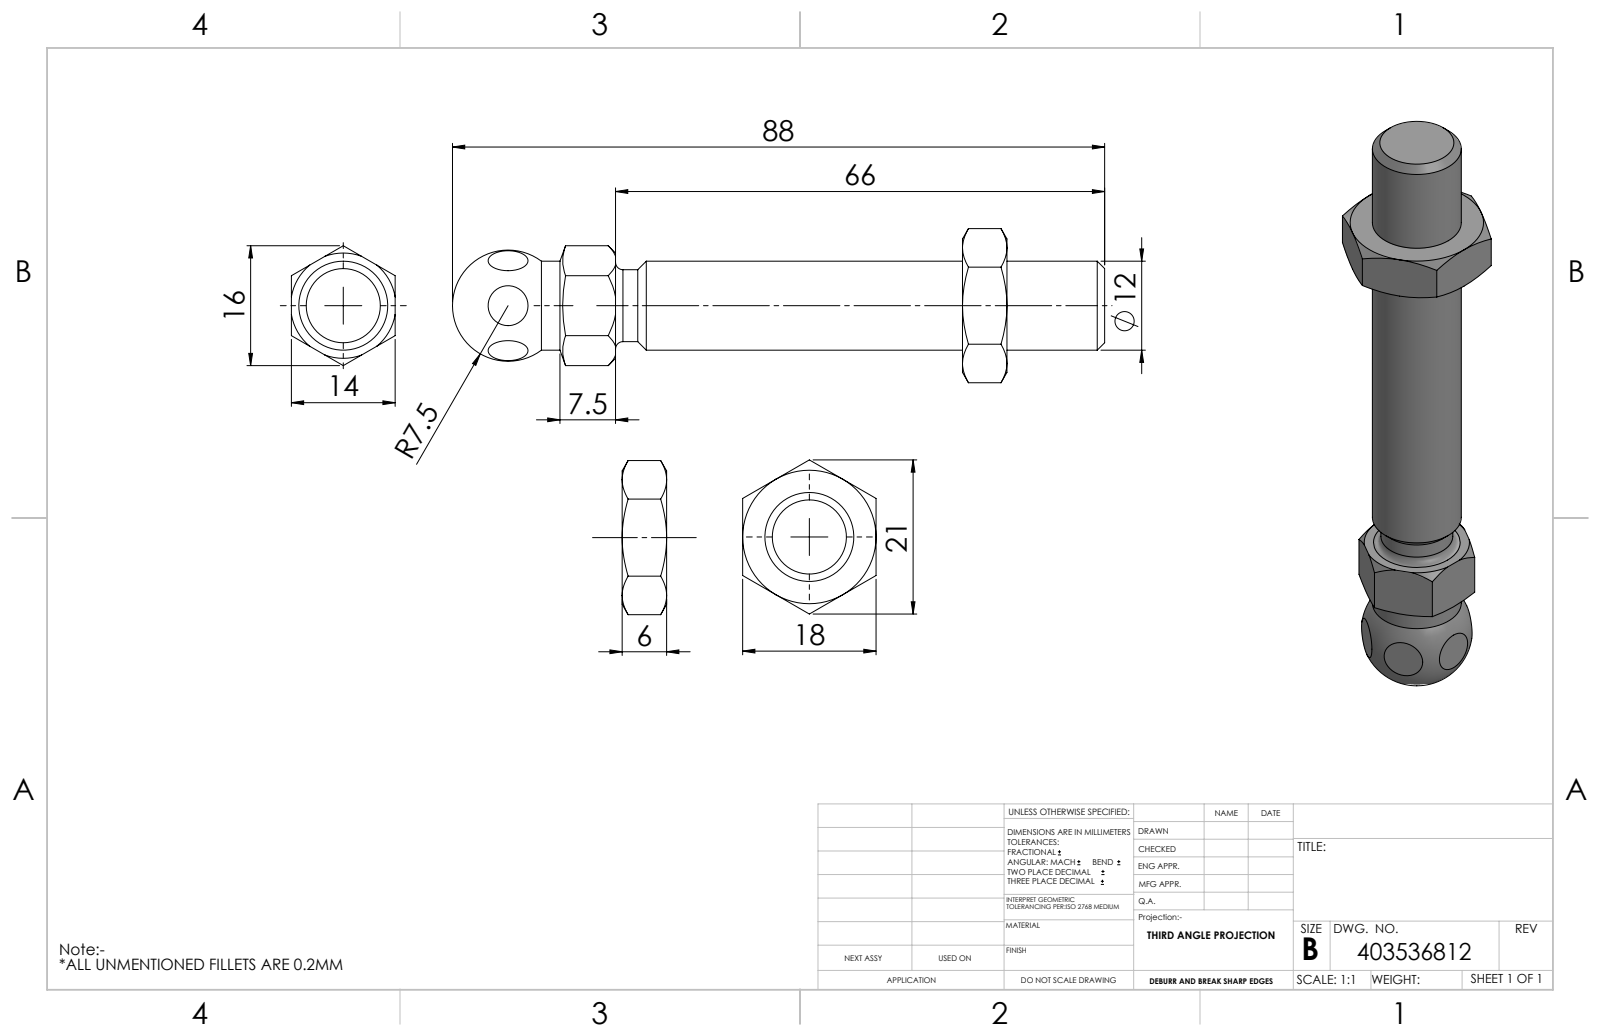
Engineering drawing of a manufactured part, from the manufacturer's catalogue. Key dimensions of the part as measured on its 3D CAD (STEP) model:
Part name (STEP PRODUCT): 403536812 Gewindestange M12x66 Edelstahl
STEP written by: Autodesk Inventor 2014 (AUTOMOTIVE_DESIGN)
Units: millimetres
Bodies: 2 solids, 52 faces (22 planar, 5 cylindrical, 25 other)
Overall size (bounding box): 88 × 20.79 × 18
Volume: 11 559 mm³ · Surface area: 4 609 mm²
Round holes (diameter × count): ⌀10.2 ×1
Round bosses / shafts (diameter × count): ⌀12 ×1, ⌀9.7 ×1
Main face-to-face distances: 2, 16, 14, 18, 6, 19.18, 13.18, 46.82, 52.82, 66
